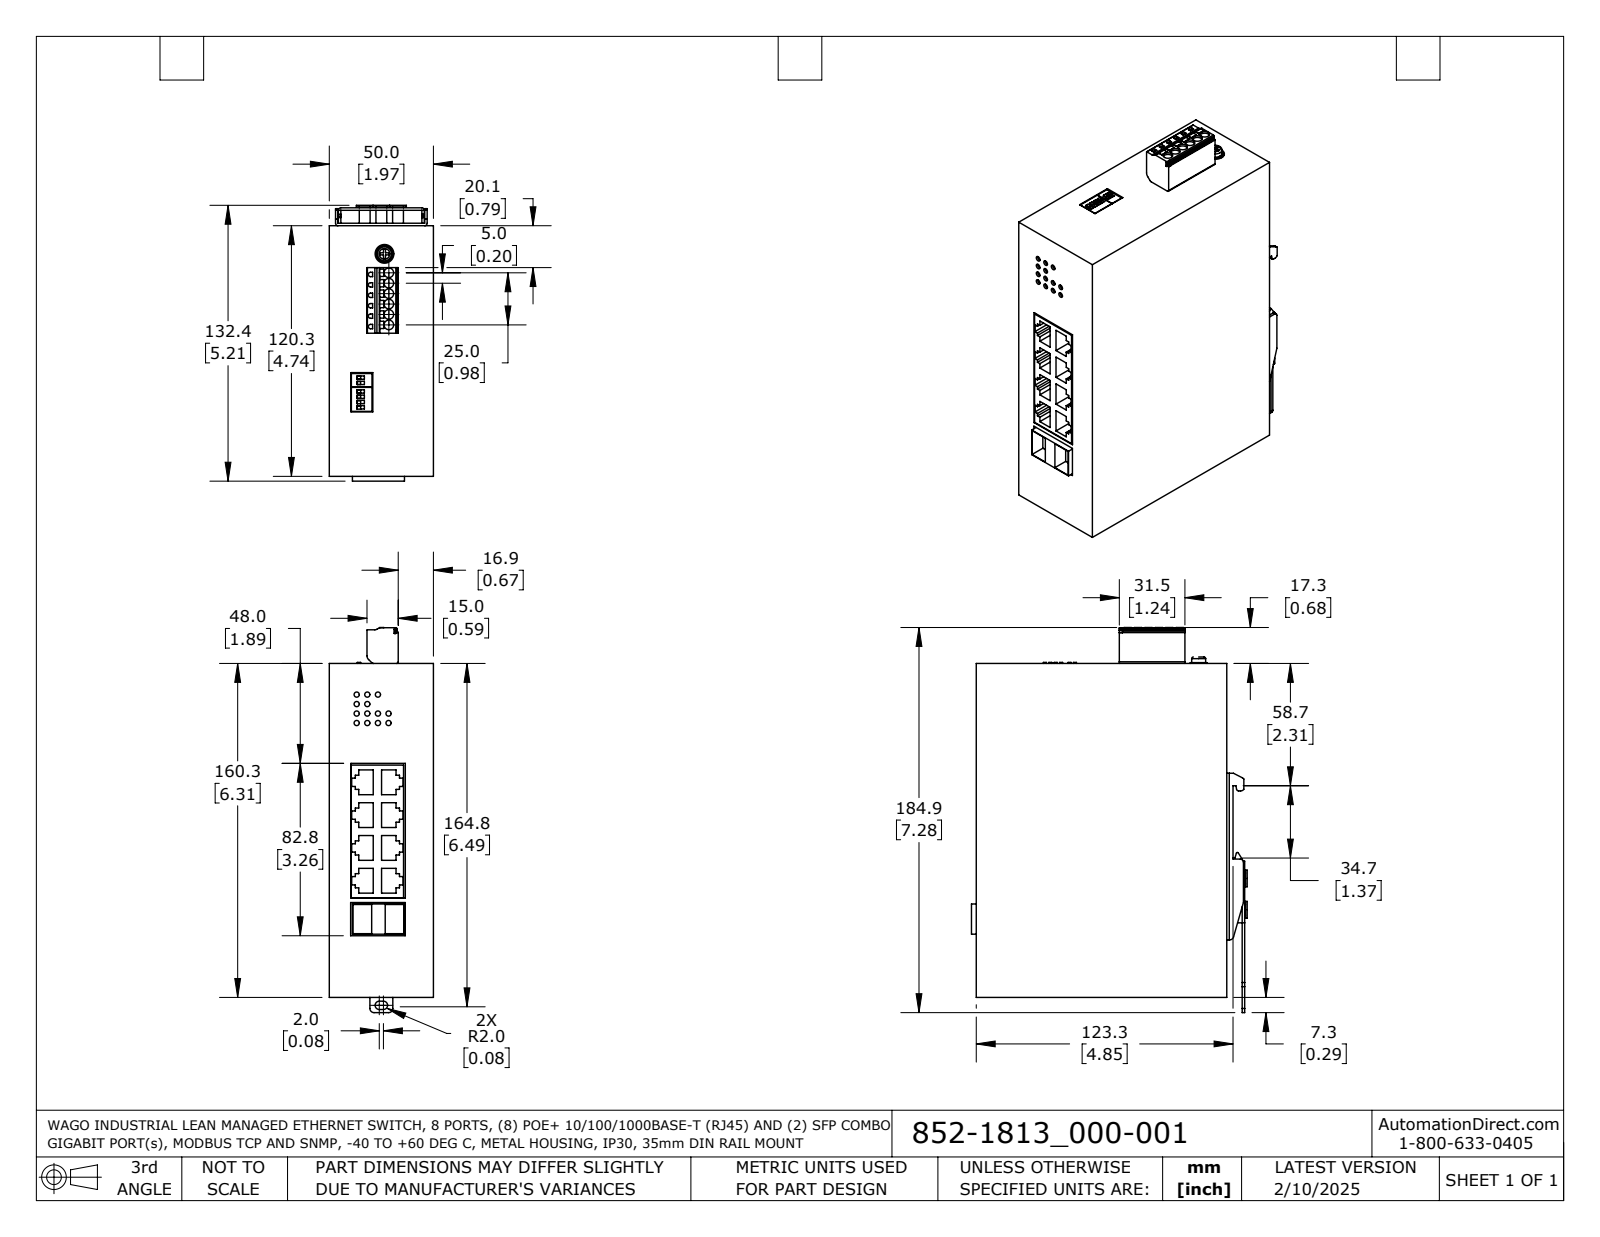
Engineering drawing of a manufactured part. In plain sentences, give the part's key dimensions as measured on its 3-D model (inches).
The part is named "852-1813_000-001". Its 3-D file was written by "SolidWorks 2021 (AUTOMOTIVE_DESIGN)". It is 1 solid with 573 faces: 407 planar, 151 cylindrical and 15 other. Overall it measures 7.278 by 5.213 by 1.969 inches. Its volume is 59.13 cubic inches and its surface area 132 square inches. Round holes: 13 of diameter 0.098, 6 of diameter 0.181, 2 of diameter 0.394, 1 of diameter 0.354. Round bosses or shafts: 4 of diameter 0.315, 3 of diameter 0.205, 1 of diameter 0.264. Partial cylindrical surfaces (rounded edges, fillets, slot ends): 14 of radius 0.004, 10 of radius 0.079, 6 of radius 0.041, 6 of radius 0.104, 5 of radius 0.047, 4 of radius 0.02, 3 of radius 0.008, 1 of radius 0.031. The main face-to-face distances are 1.969, 0.047, 6.311, 4.736, 0.291, 4.783, 0.244, 0.339, 5.028, 5.075. The hole center spacings are 0.269, 0.201, 0.179, 0.411, 0.44, 0.197, 0.358, 0.402.
